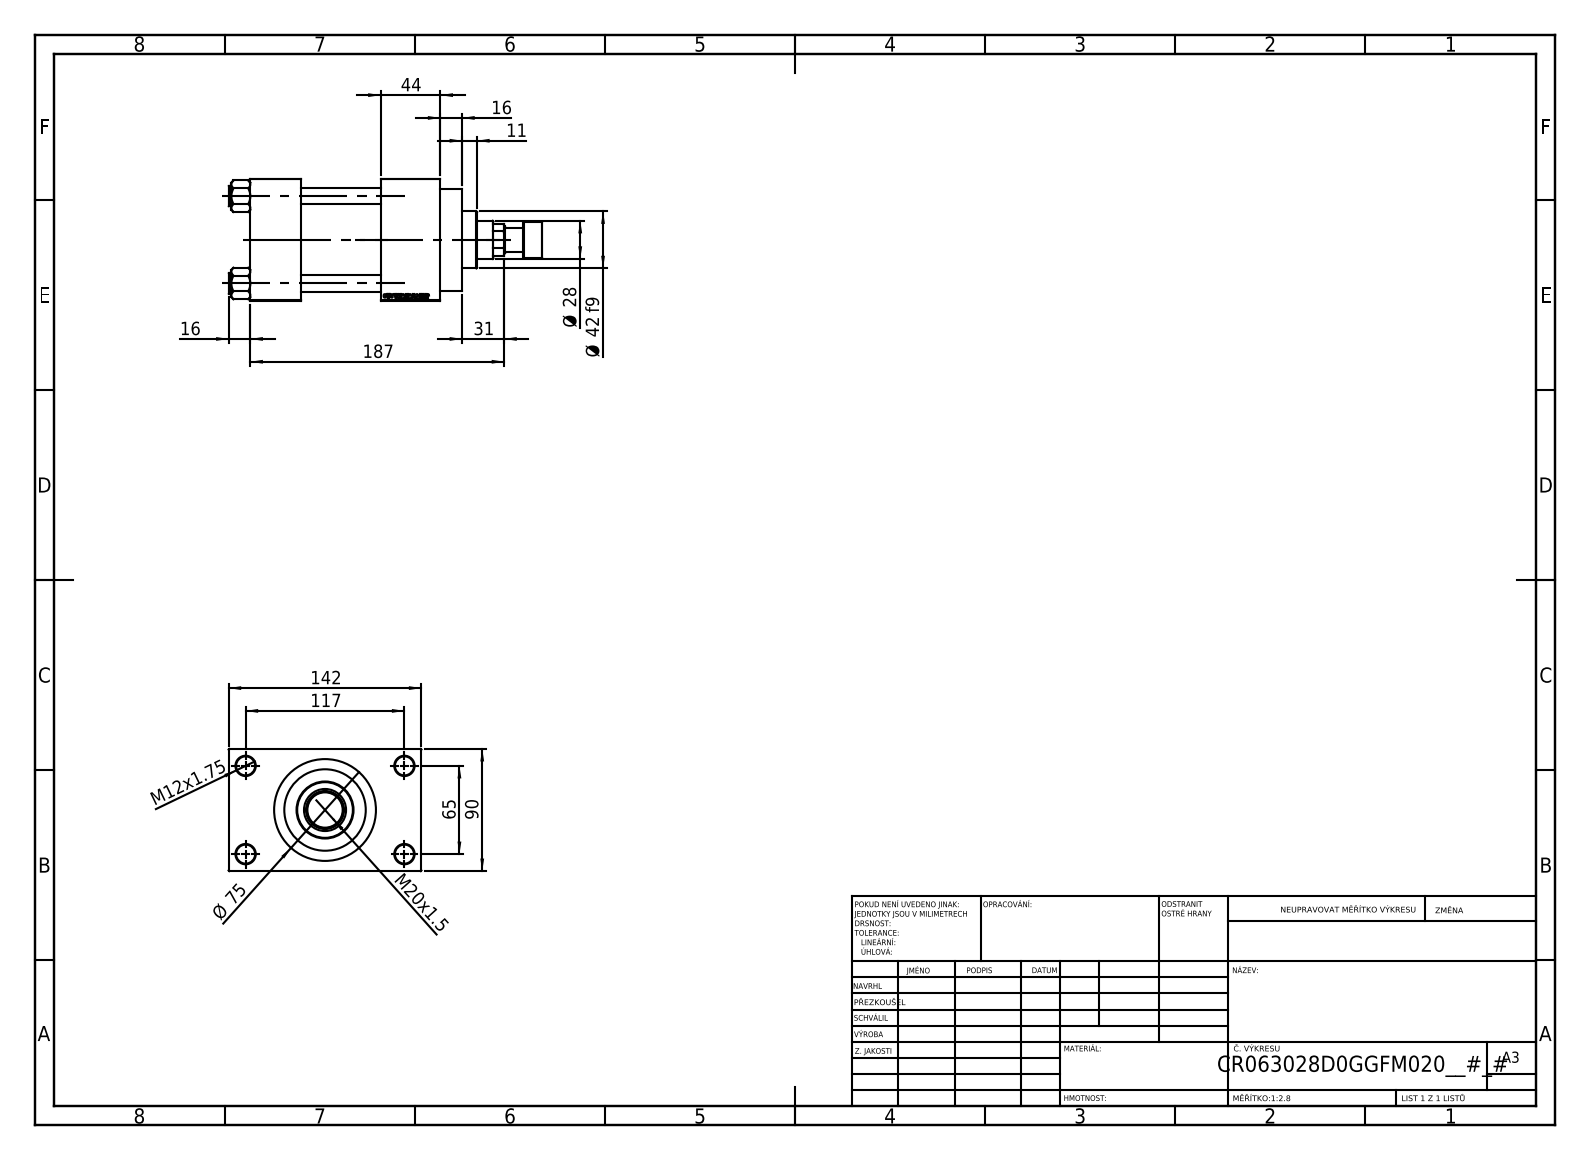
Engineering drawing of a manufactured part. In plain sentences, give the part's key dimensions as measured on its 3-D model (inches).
The part is named "V215CR_D_Body; V215CR_ROD_END_F; V215_VC_A; V215CR_D_TYCINKA (+2 more)". Its 3-D file was written by "SolidWorks 2019 (CONFIG_CONTROL_DESIGN)". It is 12 solids with 1118 faces: 501 planar, 93 cylindrical and 524 other. Overall it measures 9.094 by 5.591 by 3.543 inches. Its volume is 68.16 cubic inches and its surface area 312.9 square inches. Round holes: 4 of diameter 0.472, 4 of diameter 0.551, 2 of diameter 0.276, 2 of diameter 0.825, 2 of diameter 1.181, 1 of diameter 0.728, 1 of diameter 1.102, 1 of diameter 1.22, 1 of diameter 1.969, 1 of diameter 2.362, 1 of diameter 2.48. Round bosses or shafts: 4 of diameter 0.591, 1 of diameter 2.953, 1 of diameter 2.717, 1 of diameter 1.654, 1 of diameter 1.063, 1 of diameter 0.709. The main face-to-face distances are 3.543, 2.323, 1.457, 3.78, 5.512, 4.055, 1.732, 1.024, 4.567, 5.591. The hole center spacings are 1.037, 1.79, 2.531, 2.635, 2.748, 3.569, 4.383, 2.559.
